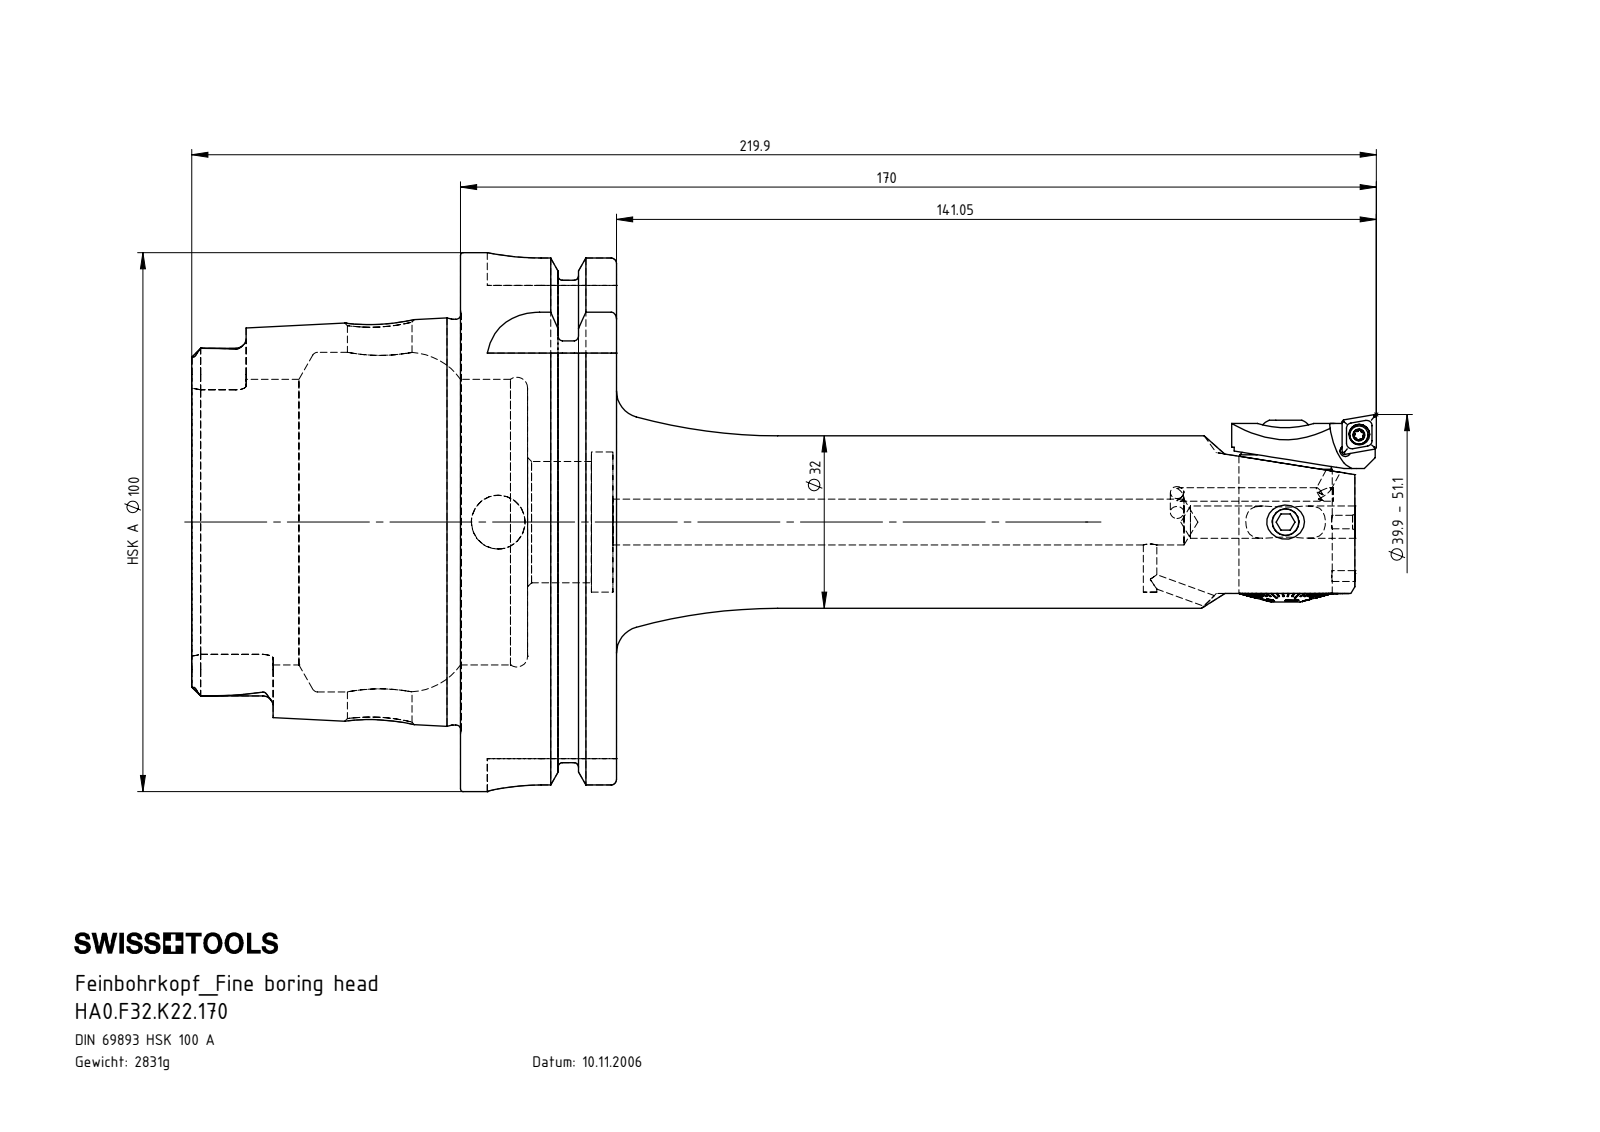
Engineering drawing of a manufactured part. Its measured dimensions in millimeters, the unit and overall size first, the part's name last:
Units: millimetres
Overall size (bounding box): 219.9 × 100 × 100
Round holes (diameter × count): ⌀1.5 ×3, ⌀2.05 ×2, ⌀3.3 ×2, ⌀5 ×2, ⌀12 ×2, ⌀2.1 ×1, ⌀2.7 ×1, ⌀2.8 ×1, ⌀2.9 ×1, ⌀3 ×1, ⌀3.85 ×1, ⌀4.2 ×1
Round bosses / shafts (diameter × count): ⌀6 ×2, ⌀2.5 ×2, ⌀100 ×1, ⌀91.95 ×1, ⌀75.26 ×1, ⌀37 ×1, ⌀16.98 ×1, ⌀16.85 ×1
Partial cylindrical surfaces — rounded edges, fillets, slot ends (radius × count): R0.21 ×6, R1.9 ×6, R0.5 ×5, R10 ×5, R0.36 ×4, R1.4 ×4, R4.88 ×4, R0.36 ×2
Main face-to-face distances: 28.95, 12.45, 16.5, 49.9, 62.35, 78.85, 215.9, 166, 153.55, 137.05
Hole centre spacings: 3.84, 4, 8, 8.72, 146.15, 153.1, 168.15
Volume: 386 224 mm³ · Surface area: 78 726 mm²
Bodies: 16 solids, 918 faces (374 planar, 194 cylindrical, 350 other)
Part name (STEP PRODUCT): ISO 4026 - M6 x 8; F32-BG2.014.012_A; F32-BG1.AA4.017_Standart; F32-BG3.006.026_A (+8 more)
STEP written by: SolidWorks 2022 (CONFIG_CONTROL_DESIGN)
